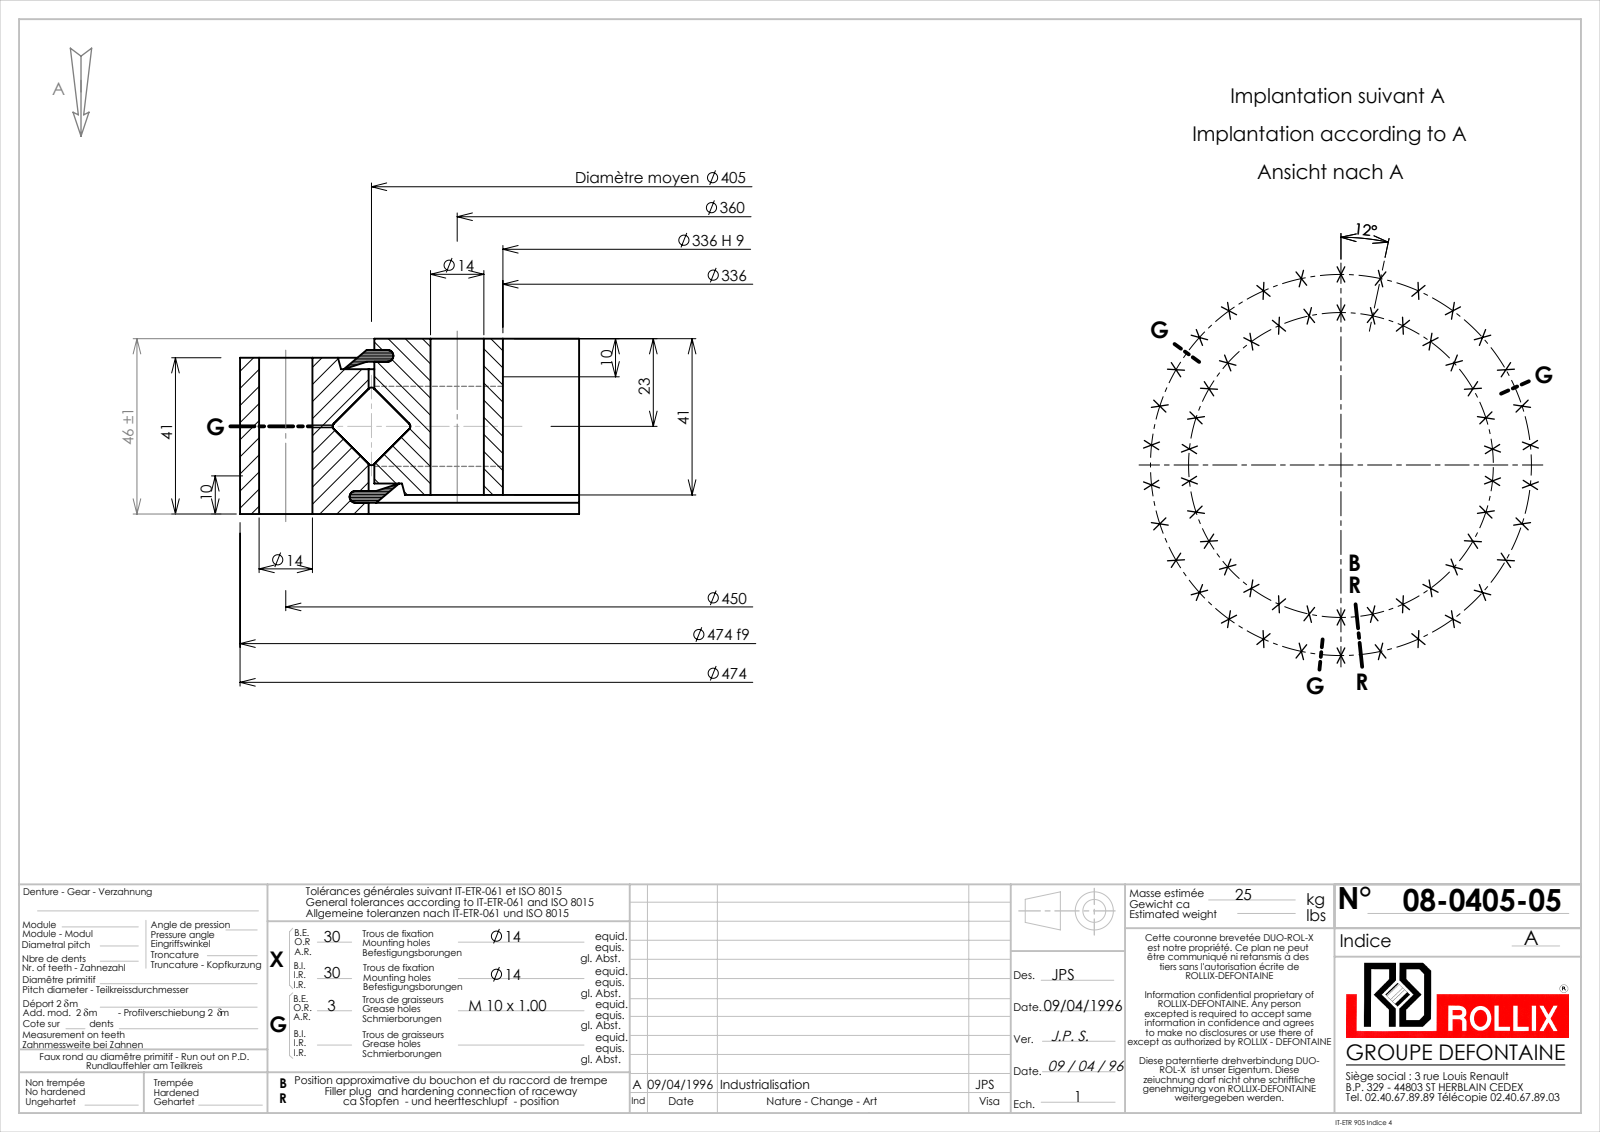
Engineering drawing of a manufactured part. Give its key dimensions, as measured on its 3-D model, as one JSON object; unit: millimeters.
{"part_name": "08-0405-05", "step_written_by": "SolidWorks 2016 (CONFIG_CONTROL_DESIGN)", "units": "millimeters", "bodies": {"solids": 5, "faces": 204, "planar": 16, "cylindrical": 144, "other": 44}, "overall_size": [474, 474, 46], "volume_mm3": 2875000, "surface_area_mm2": 589106, "round_holes": [[14, 60], [9, 3], [336, 1], [406.5, 1]], "round_bosses_or_shafts": [[474, 1], [403.5, 1], [15, 1]], "face_to_face_distances": [5, 41, 46, 36, 6.05, 39.95, 1.05, 34.95, 2.95, 43.05], "hole_center_spacings": [225, 364.06, 47.04, 93.56, 139.06, 183.03, 301.11, 440.17]}
